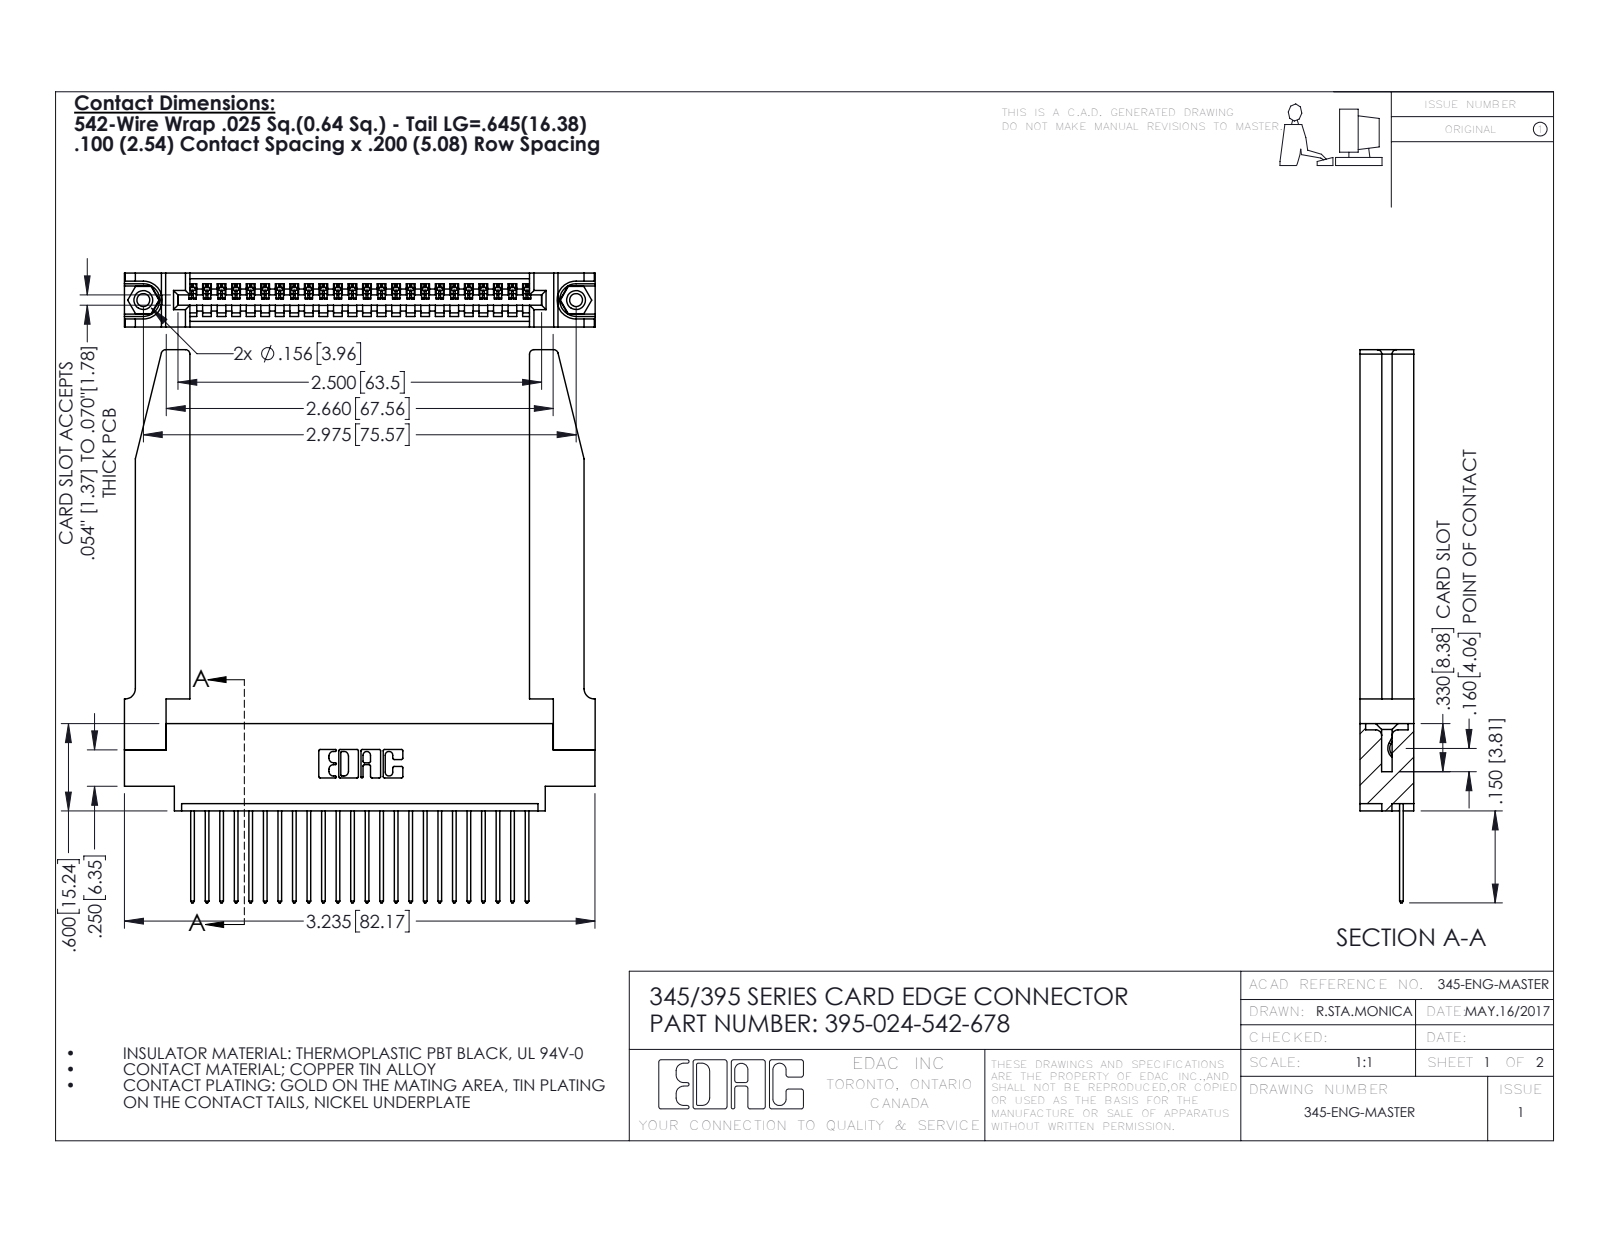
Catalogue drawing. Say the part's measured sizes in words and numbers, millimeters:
The part is named "395-024-542-678; 345 Part_0.170 Offset - 0.156 Dia-TH; 345-250-001_345-250-001-102; 345-292-001_345-293-142 (+1 more)". Its 3-D file was written by "SolidWorks 2016 (CONFIG_CONTROL_DESIGN)". It is 29 solids with 1756 faces: 1186 planar, 518 cylindrical and 52 other. Overall it measures 96.6 by 82.2 by 9.4 millimeters. Its volume is 15 400 cubic millimeters and its surface area 17 160 square millimeters. Round holes: 2 of diameter 2.3, 2 of diameter 3.2, 2 of diameter 4, 1 of diameter 1.6. Round bosses or shafts: 2 of diameter 3.9. Partial cylindrical surfaces (rounded edges, fillets, slot ends): 48 of radius 0.2, 48 of radius 0.3, 22 of radius 0.3, 8 of radius 0.8, 6 of radius 0.2, 6 of radius 0.8, 3 of radius 0.7, 2 of radius 0.8. The main face-to-face distances are 9.4, 1.8, 7.6, 2.5, 6.9, 0.6, 5.1, 3.8, 3.8, 3.1. The hole center spacings are 6.9, 69.6, 75.6.
